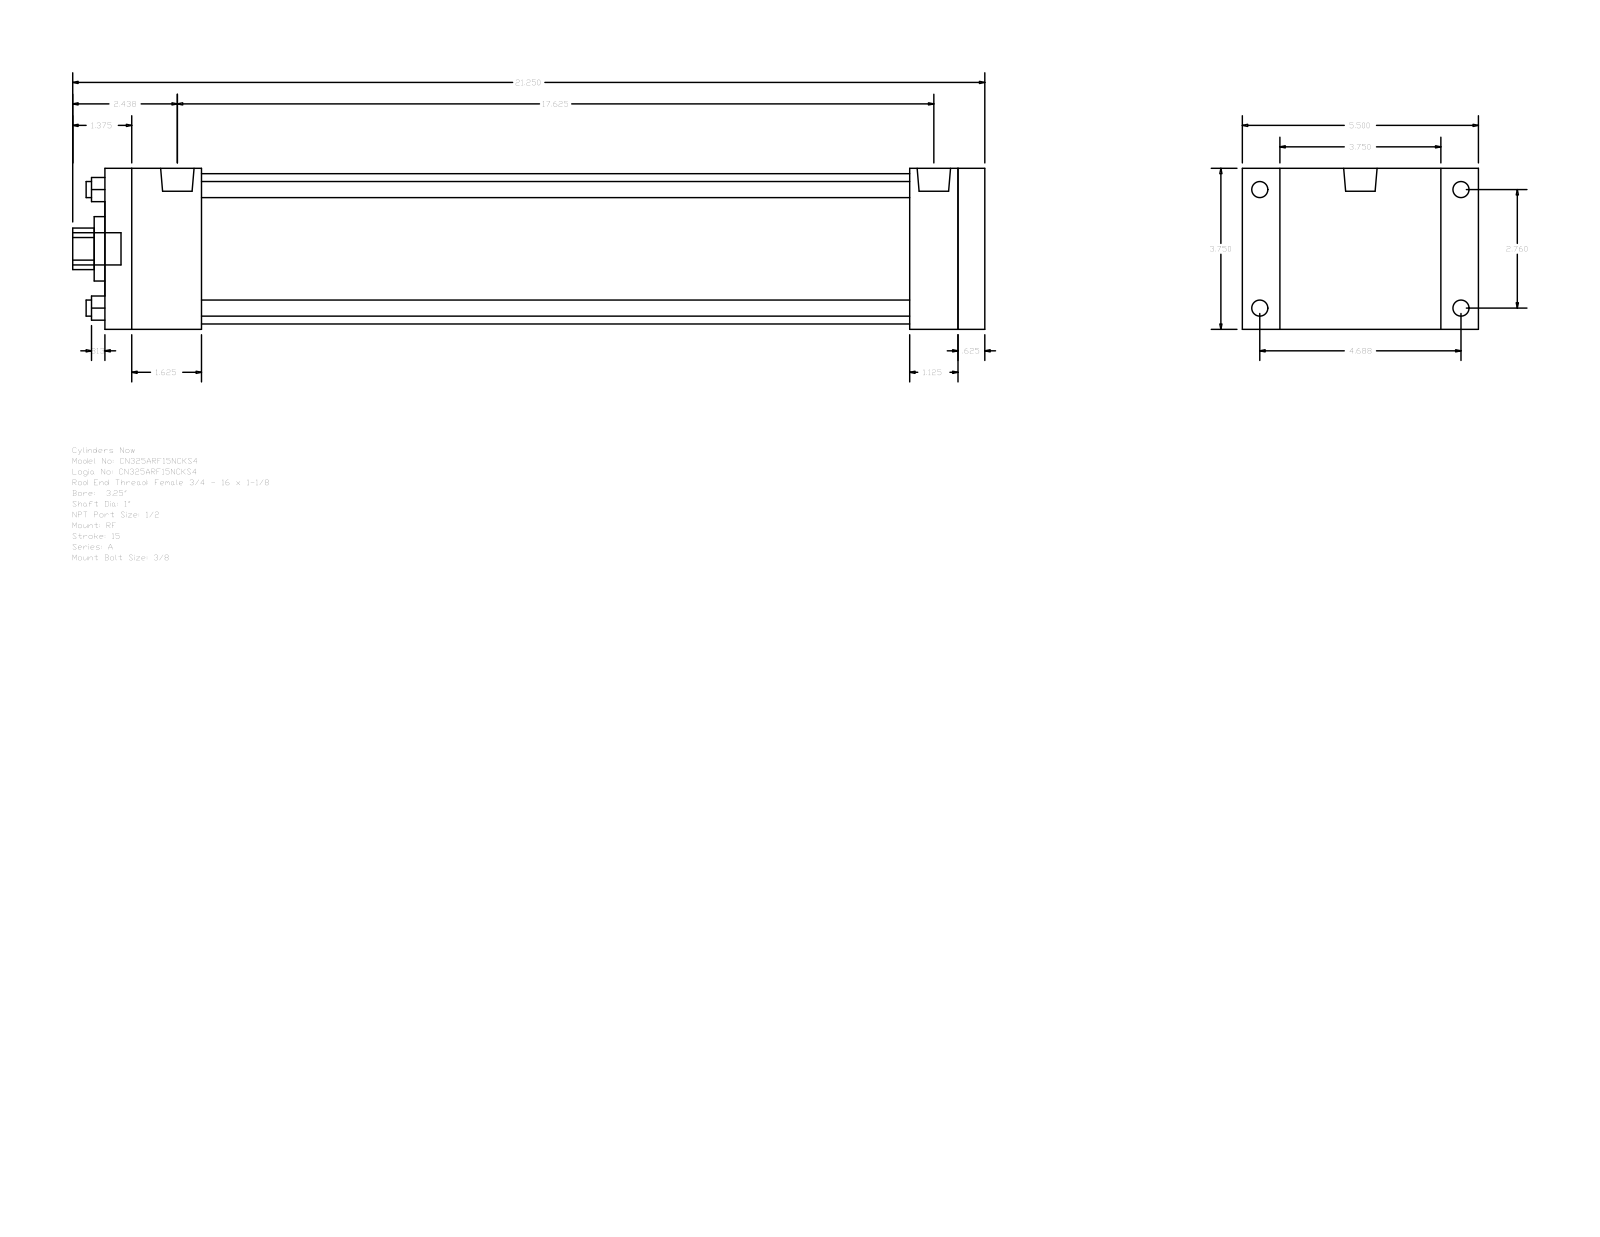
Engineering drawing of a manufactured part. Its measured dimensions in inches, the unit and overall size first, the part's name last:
Units: inches
Overall size (bounding box): 21.25 × 5.5 × 3.75
Round holes (diameter × count): ⌀0.375 ×4, ⌀1 ×1, ⌀1.5 ×1, ⌀3.5 ×1
Round bosses / shafts (diameter × count): ⌀0.375 ×4, ⌀0.344 ×4, ⌀0.778 ×2, ⌀0.75 ×1
Partial cylindrical surfaces — rounded edges, fillets, slot ends (radius × count): R0.484 ×1
Main face-to-face distances: 3.75, 20.5, 0.625, 19.875, 0.875, 4.625, 18.75, 1.125, 1.75, 2.25
Hole centre spacings: 1.952, 2.76, 3.903
Bodies: 0 solids, 92 faces (64 planar, 28 cylindrical, 0 other)
Part name (STEP PRODUCT): A_RF__0325_1
STEP written by: GSSL Pune (CONFIG_CONTROL_DESIGN)
